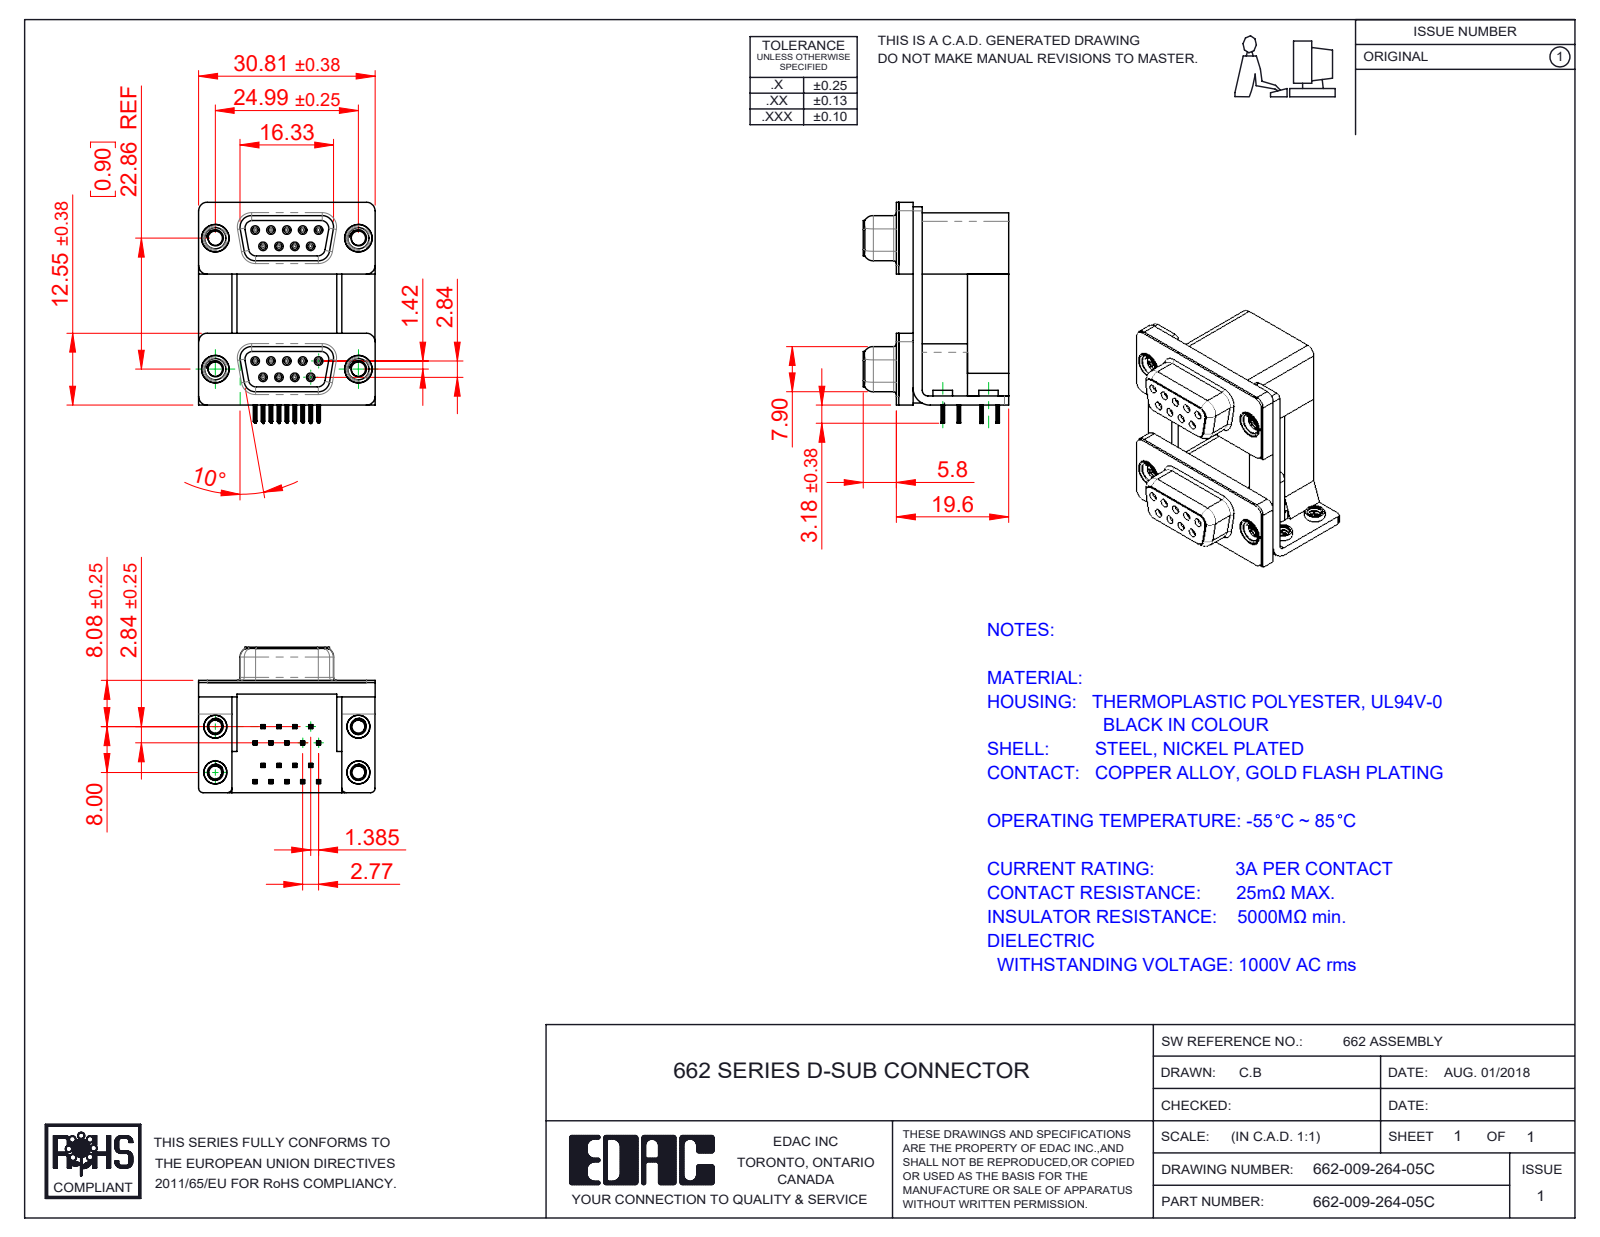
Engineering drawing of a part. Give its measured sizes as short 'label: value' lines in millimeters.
name: 662 Contact Bottom Lower; 662 Housing Lower_09 Contacts; 662 Contact Bottom Upper_H; 662 4-40 Threaded Board Mount (+8 more)
written by: SolidWorks 2020 (CONFIG_CONTROL_DESIGN)
unit: mm
bodies: 33 solids, 3254 faces (1386 planar, 880 cylindrical, 988 other)
size: 38.59 × 30.81 × 25.4
volume: 11 864 mm³; area: 13 984 mm²
holes: 18× ⌀0.8, 18× ⌀0.9, 4× ⌀2.26, 4× ⌀2.5, 4× ⌀2.75, 4× ⌀3.2, 4× ⌀3.5, 4× ⌀4, 4× ⌀4.8, 4× ⌀5
bosses: 18× ⌀1.2, 4× ⌀4.9, 4× ⌀4.75, 4× ⌀4, 4× ⌀3.9, 4× ⌀3.4
rounds: 144× R0.1, 72× R0.15, 36× R0.35, 18× R0.34, 16× R1.35, 13× R1.5, 8× R0.28, 8× R0.5
face distances: 2.5, 16.7, 19.2, 0.4, 22.86, 9.5, 7.2, 12, 2.9, 1.6
hole spacings: 3.16, 2.77, 23.03, 22.86, 5.54, 23.52, 20.07, 25.74
